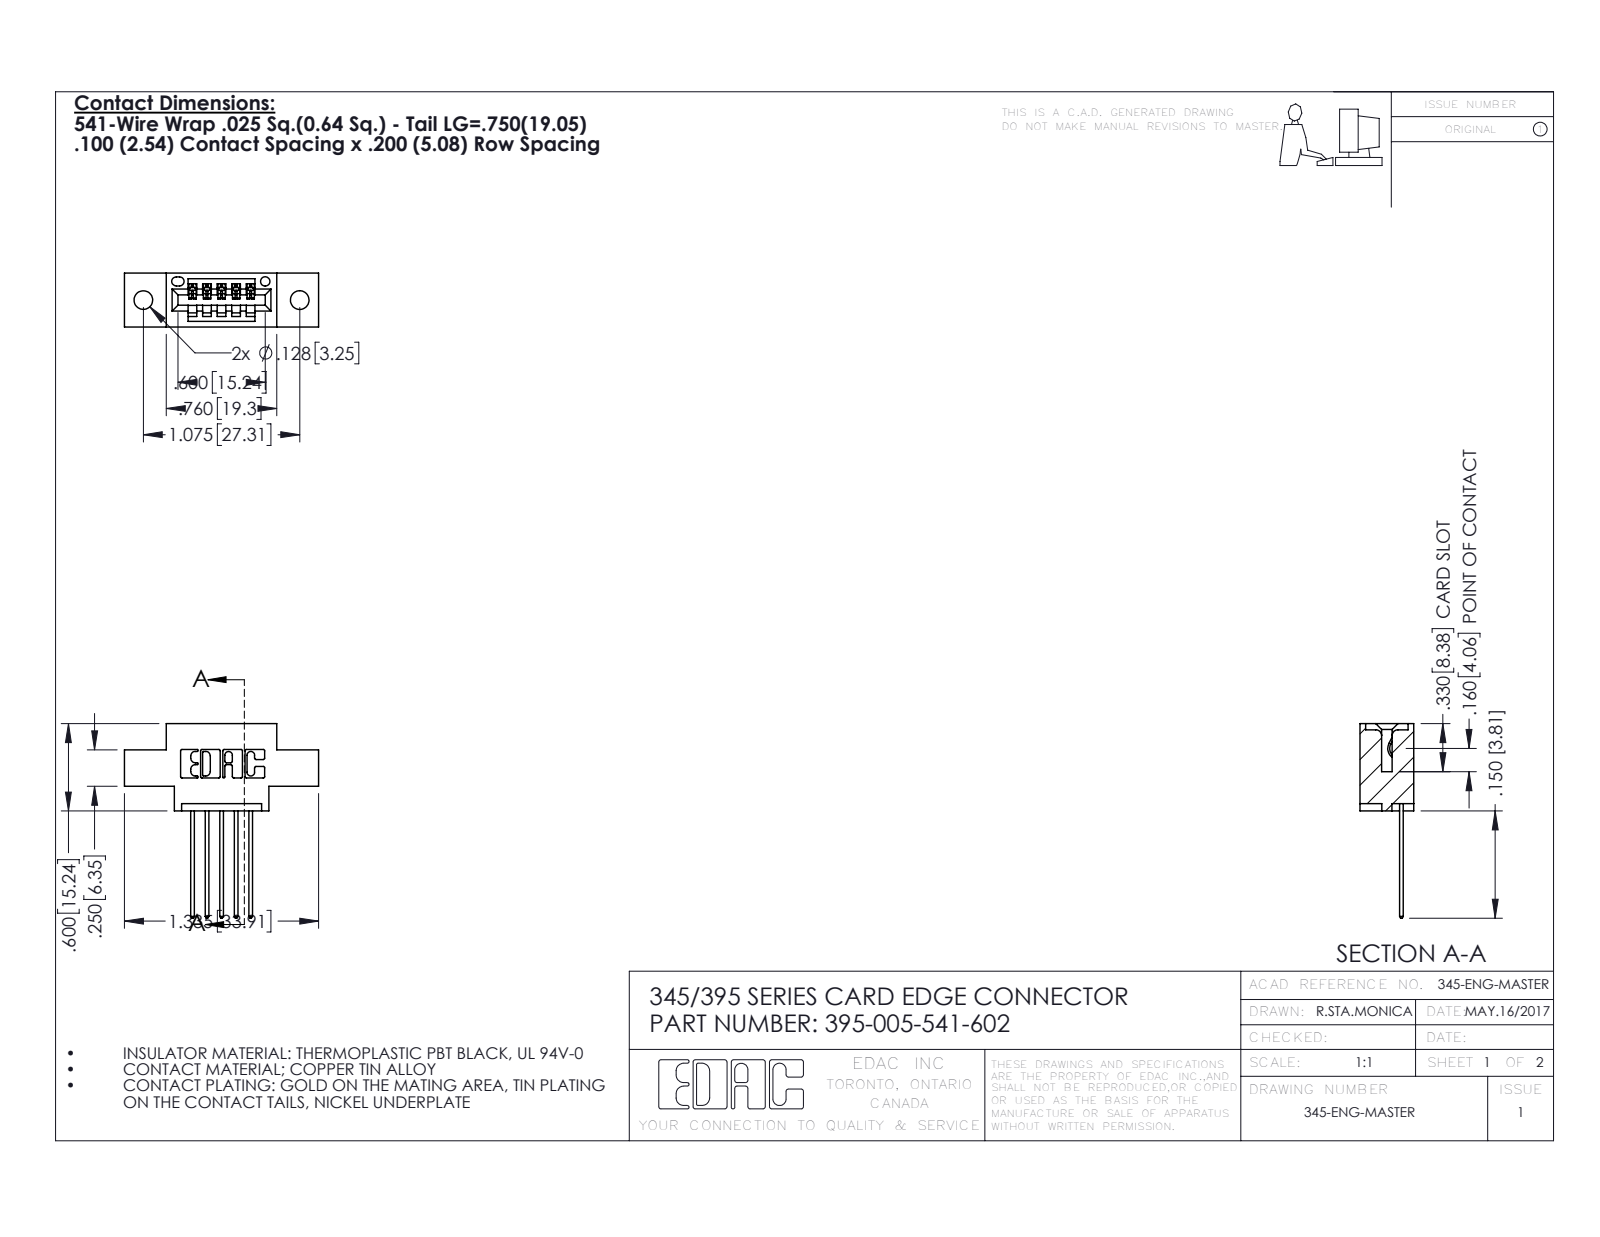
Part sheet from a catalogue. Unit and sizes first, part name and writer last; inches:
Units: inches
Overall size (bounding box): 1.337 × 1.335 × 0.37
Round holes (diameter × count): ⌀0.128 ×2, ⌀0.064 ×1
Partial cylindrical surfaces — rounded edges, fillets, slot ends (radius × count): R0.01 ×22, R0.006 ×10, R0.01 ×10, R0.007 ×6, R0.031 ×6, R0.026 ×3, R0.031 ×2, R0.04 ×2
Main face-to-face distances: 0.37, 0.2, 0.298, 0.072, 0.1, 0.025, 0.098, 0.272, 0.25, 0.06
Hole centre spacings: 0.27, 0.847, 1.075
Volume: 0.17 in³ · Surface area: 4.881 in²
Bodies: 6 solids, 420 faces (284 planar, 136 cylindrical, 0 other)
Part name (STEP PRODUCT): 345-292-001_345-293-141; 395-005-541-602; 345 Part_0.170 Offset - 0.128 Dia
STEP written by: SolidWorks 2016 (CONFIG_CONTROL_DESIGN)
